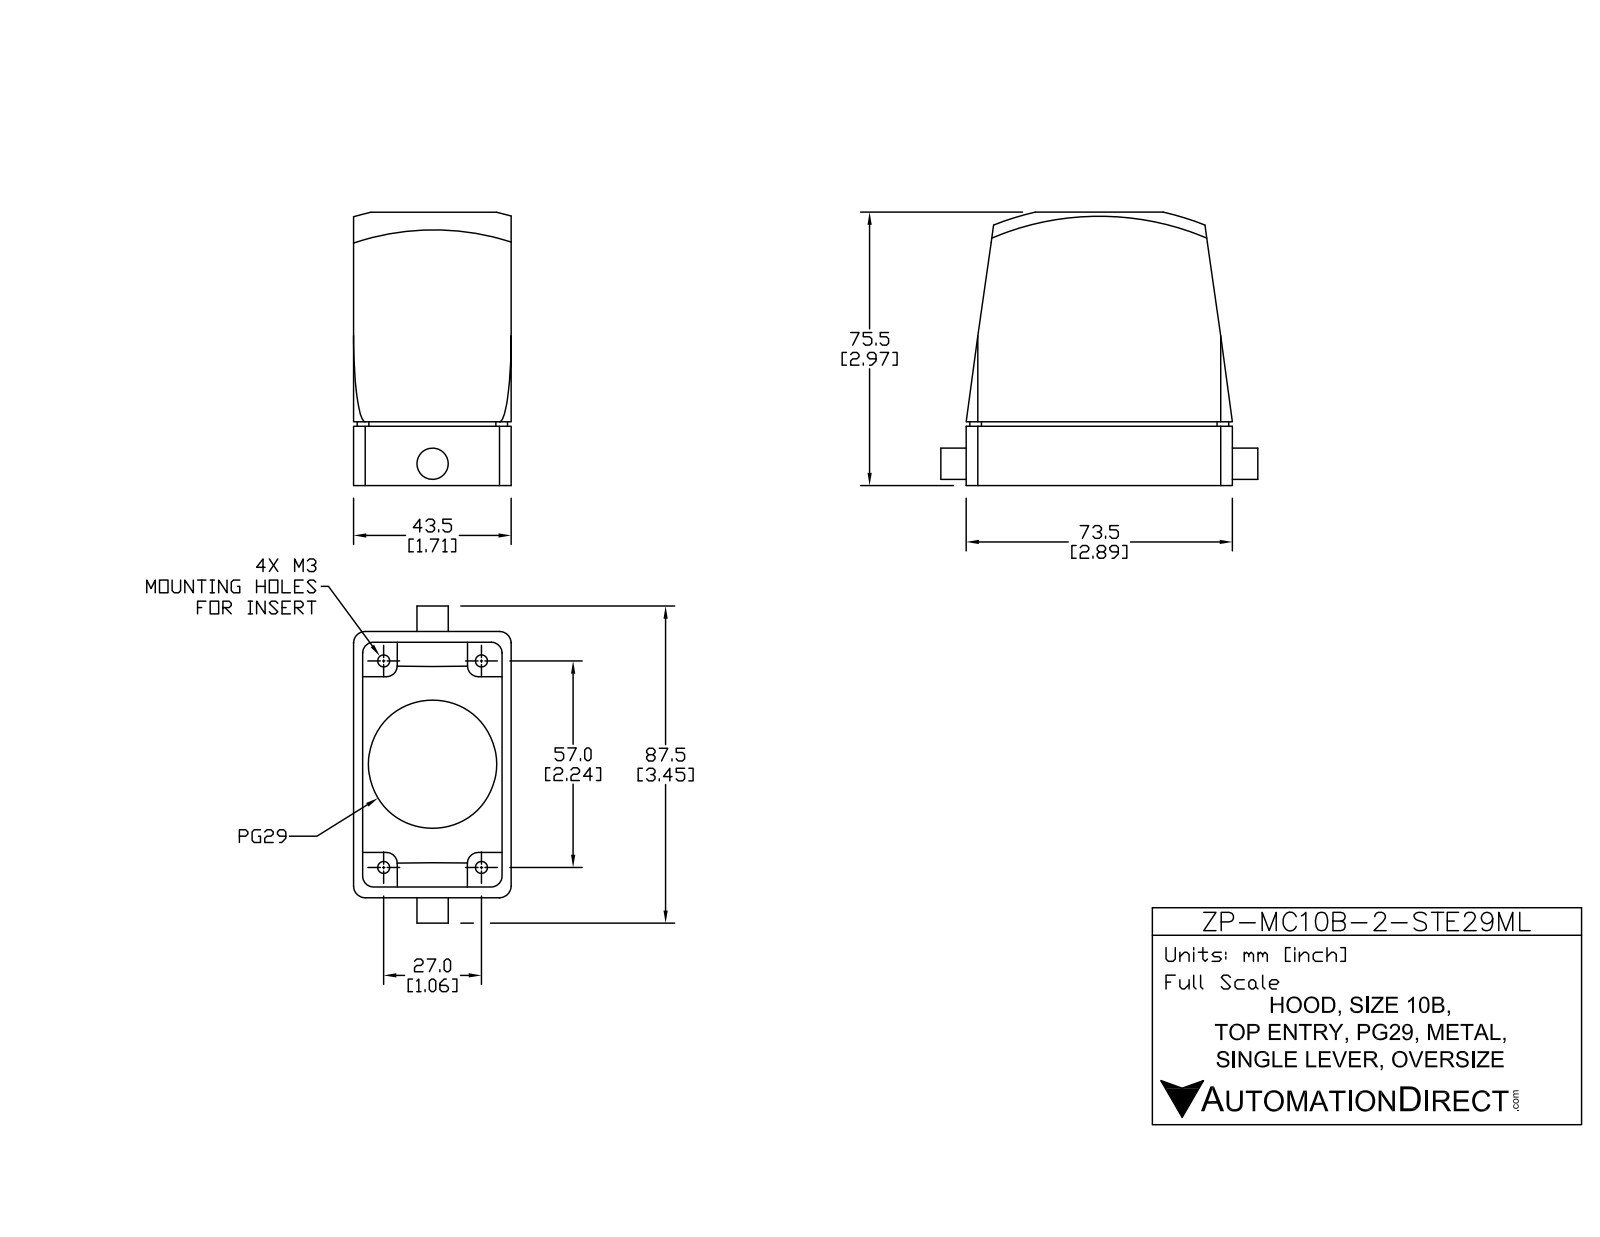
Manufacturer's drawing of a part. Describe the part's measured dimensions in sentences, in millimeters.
The part is named "ZP-MC10B-2-STE29ML". Its 3-D file was written by "SolidWorks 2011 (AUTOMOTIVE_DESIGN)". It is 5 solids with 86 faces: 52 planar, 28 cylindrical and 6 other. Overall it measures 87.5 by 75.63 by 43.5 millimeters. Its volume is 57 273 cubic millimeters and its surface area 43 169 square millimeters. Round holes: 4 of diameter 3.5, 1 of diameter 35.5. Round bosses or shafts: 1 of diameter 8.6. Partial cylindrical surfaces (rounded edges, fillets, slot ends): 8 of radius 3.2, 4 of radius 0.7, 4 of radius 3. The main face-to-face distances are 2.5, 41, 43.5, 38.5, 9.5, 58.08, 2.96, 12.46, 61.04, 70.54. The hole center spacings are 32.86, 28.96, 59, 65.72.
